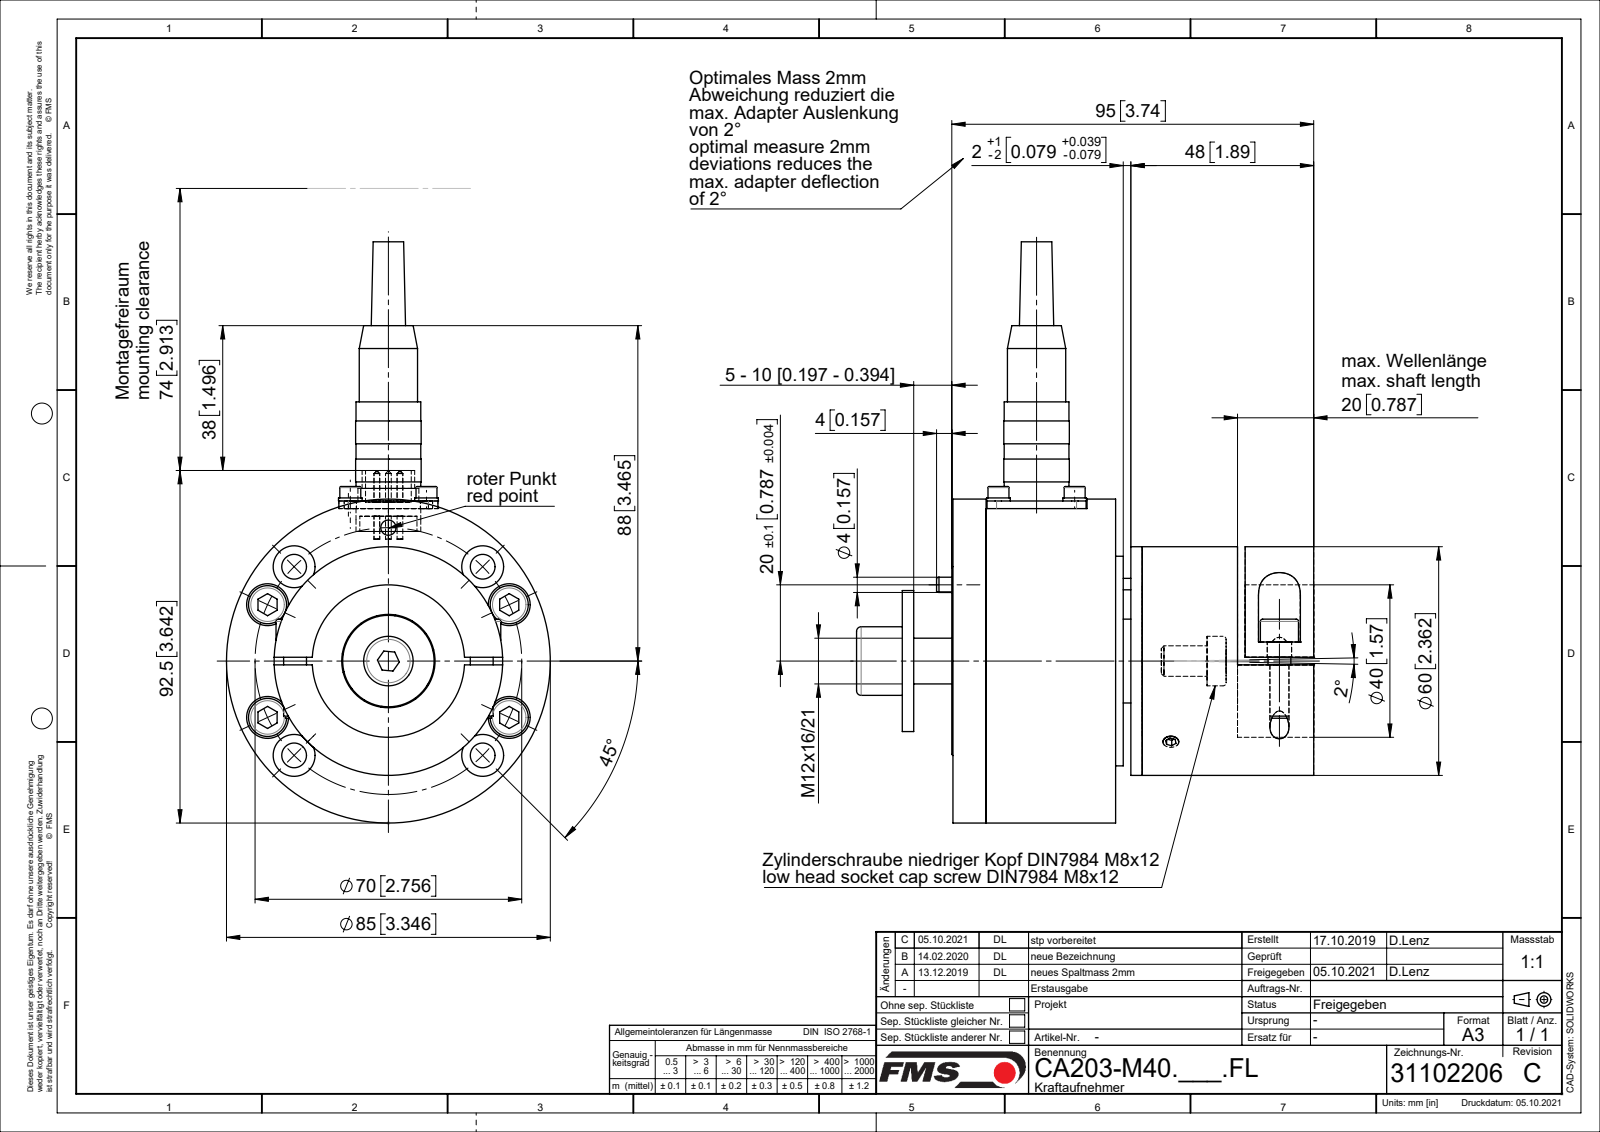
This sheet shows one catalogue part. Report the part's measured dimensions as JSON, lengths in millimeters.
{"part_name": "Zyl-Schr DIN912_M3x6; RKL_6203_01; Spannstift_ISO13337_D04x10; Zyl-Schr DIN912_M6x20 (+8 more)", "step_written_by": "SolidWorks 2018 (CONFIG_CONTROL_DESIGN)", "units": "millimeters", "bodies": {"solids": 43, "faces": 785, "planar": 270, "cylindrical": 326, "other": 189}, "overall_size": [152.5, 120, 85], "volume_mm3": 298532, "surface_area_mm2": 111327, "round_holes": [[2.5, 8], [6.5, 8], [11, 8], [5, 6], [4, 5], [3.1, 4], [3.2, 4], [3.6, 4], [7, 4], [3, 2], [6.4, 2], [4.2, 1]], "round_bosses_or_shafts": [[3, 8], [6, 7], [10, 6], [1.5, 5], [6.2, 4], [5.7, 4], [5.5, 4], [85, 1]], "partial_cylinders_radius": [[2.5, 4], [5, 2], [5.5, 2]], "face_to_face_distances": [2, 41, 10, 30, 45, 3, 22, 60, 50, 34], "hole_center_spacings": [35, 20, 24.78, 25.2, 32.8, 51.14, 56.46, 28.28]}
